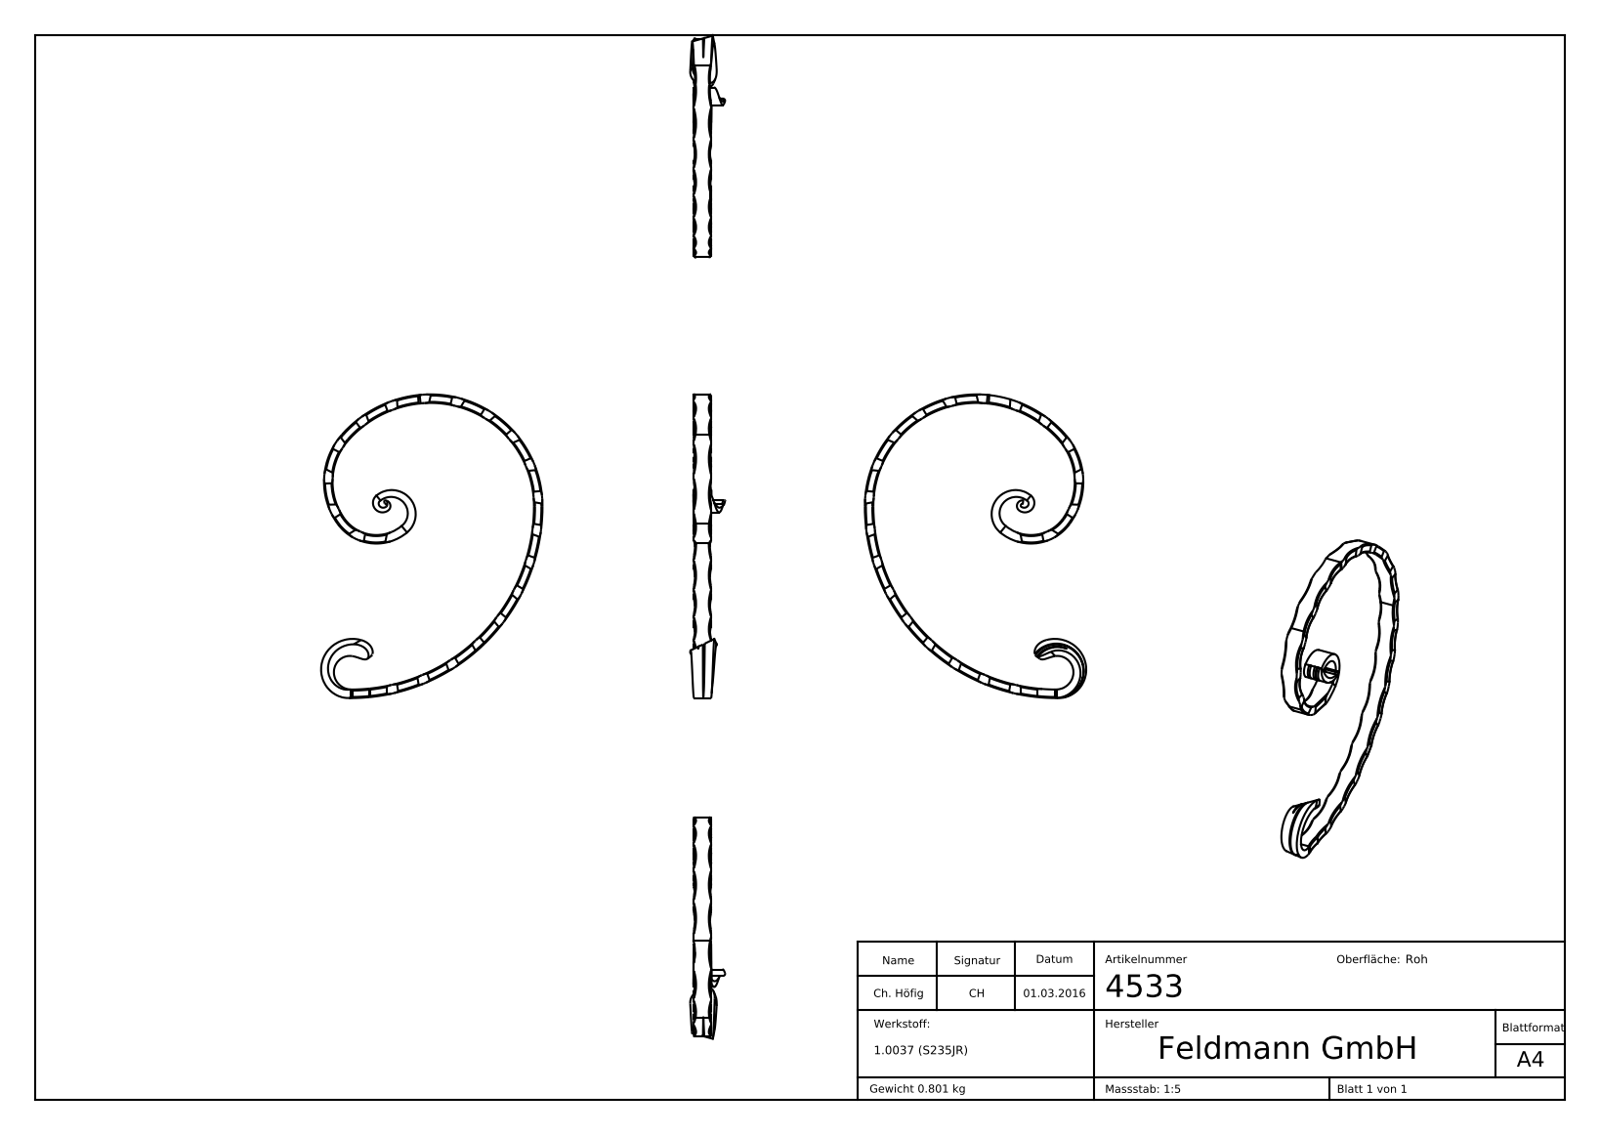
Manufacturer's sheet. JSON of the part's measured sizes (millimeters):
{"part_name": "4533", "step_written_by": "SolidWorks 2015 (CONFIG_CONTROL_DESIGN)", "units": "millimeters", "bodies": {"solids": 1, "faces": 415, "planar": 146, "cylindrical": 58, "other": 211}, "overall_size": [284.97, 207.75, 32.74], "volume_mm3": 104687, "surface_area_mm2": 40374, "partial_cylinders_radius": [[50.5, 44], [1, 2], [37, 1], [45, 1], [59, 1], [67, 1], [97, 1], [104, 1]], "face_to_face_distances": [16, 1.19, 2.66, 0.66, 0.5, 0.8, 0.53, 1.3, 0.61, 1.64]}
